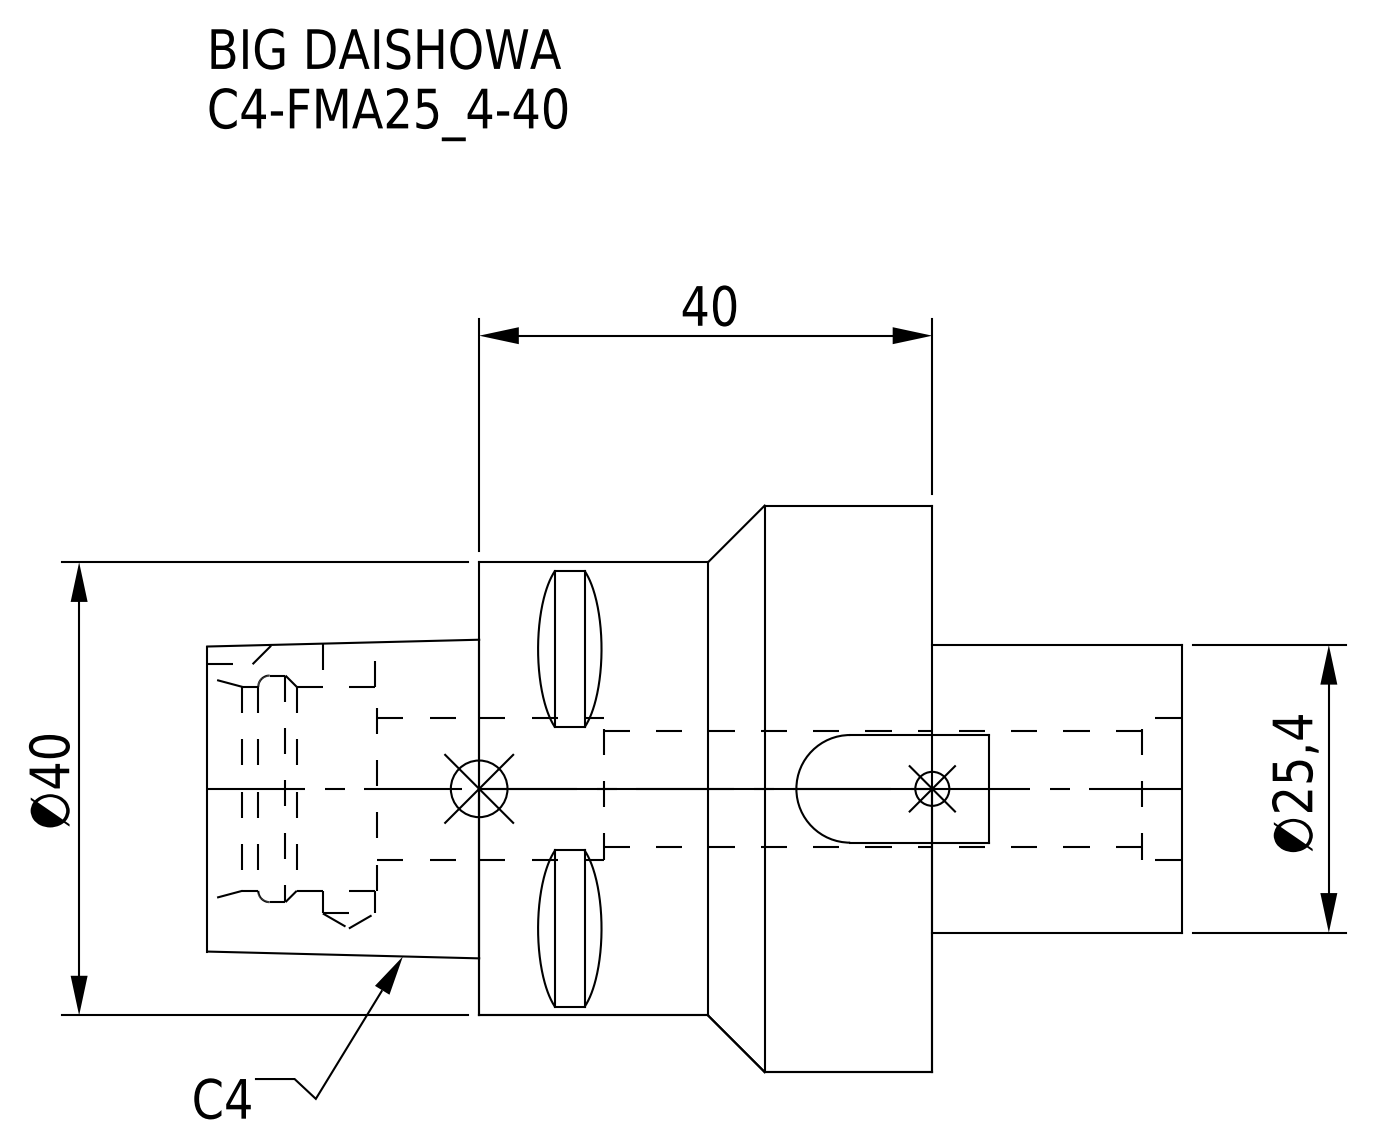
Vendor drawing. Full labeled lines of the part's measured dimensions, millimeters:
Part name (STEP PRODUCT): C4-FMA25_4-40
STEP written by: CREO PARAMETRIC BY PTC INC, 2016380 (AUTOMOTIVE_DESIGN)
Units: millimetres
Bodies: 1 solid, 74 faces (39 planar, 23 cylindrical, 12 other)
Overall size (bounding box): 86 × 50 × 50
Volume: 77 247 mm³ · Surface area: 16 627 mm²
Round holes (diameter × count): ⌀4.6 ×1, ⌀10.25 ×1, ⌀12.5 ×1, ⌀18 ×1, ⌀20 ×1
Round bosses / shafts (diameter × count): ⌀50 ×1, ⌀40 ×1, ⌀25.4 ×1
Partial cylindrical surfaces — rounded edges, fillets, slot ends (radius × count): R3 ×1
Main face-to-face distances: 40, 22, 62, 17, 5, 45, 86, 69, 64, 24
